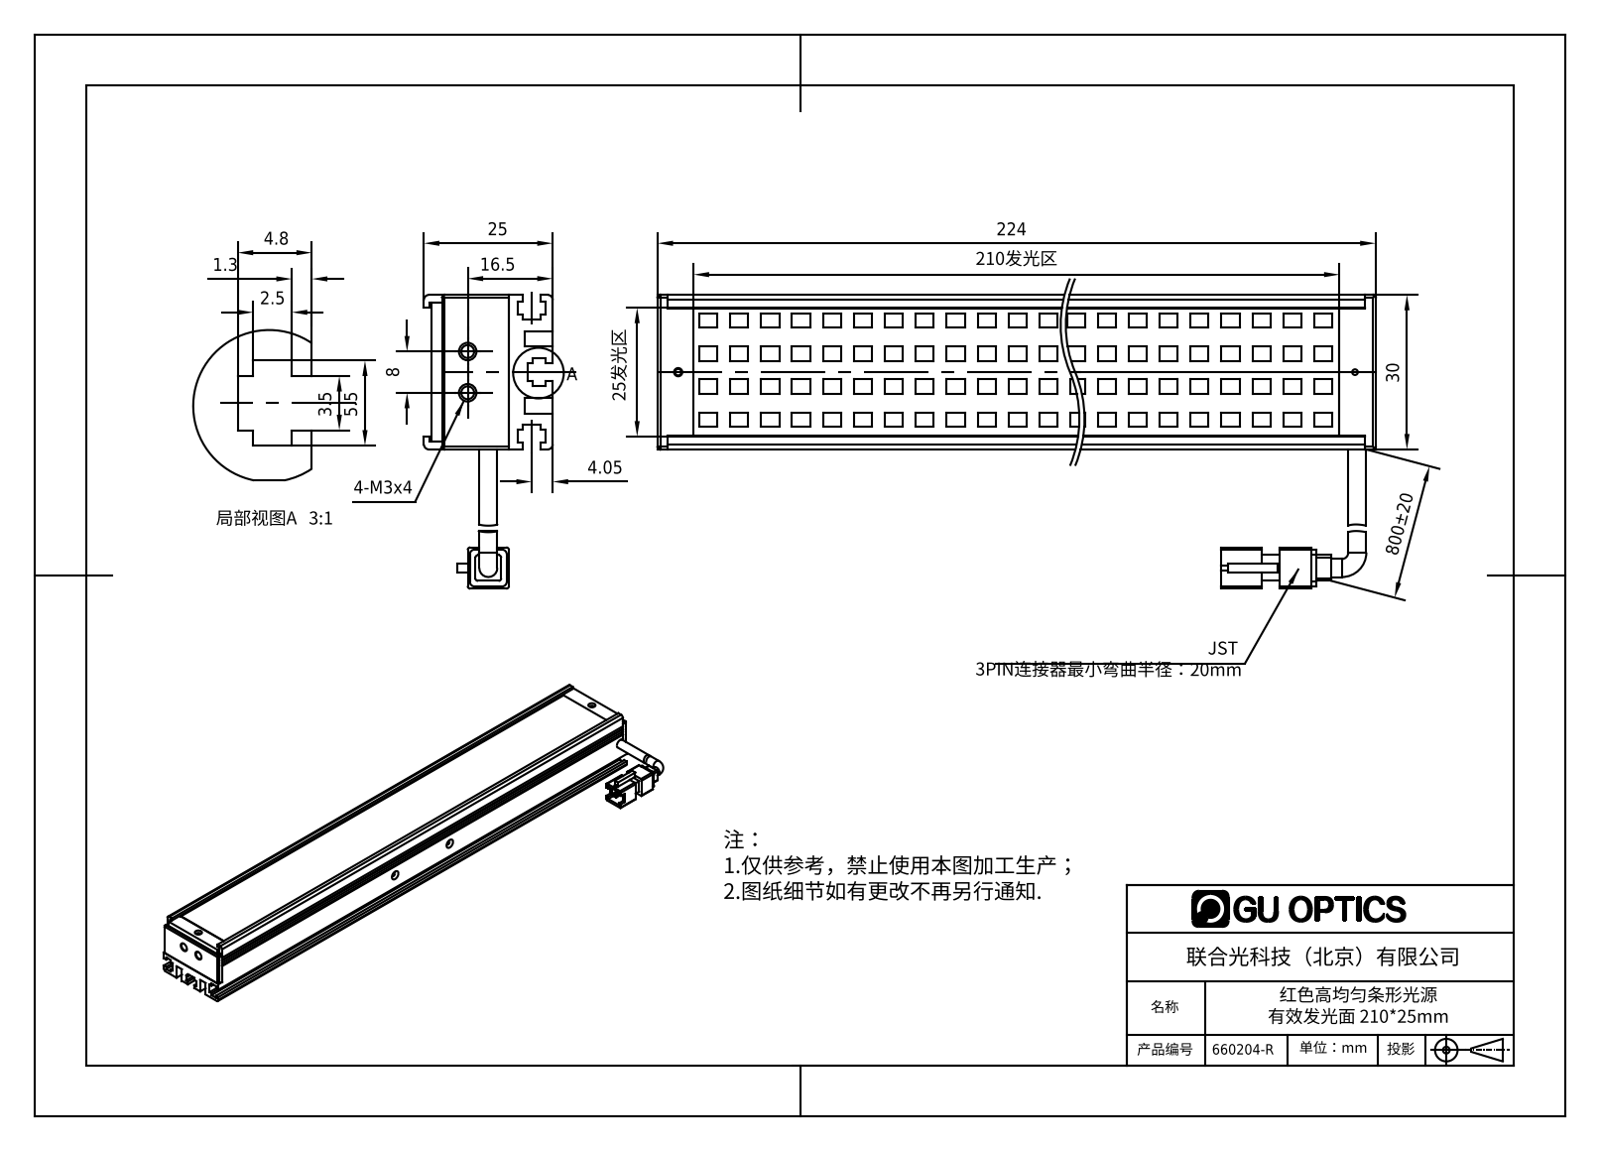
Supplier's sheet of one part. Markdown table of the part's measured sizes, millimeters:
| quantity | value |
| --- | --- |
| part name | 660204-R |
| STEP written by | SolidWorks 2016 (AUTOMOTIVE_DESIGN) |
| units | millimeters |
| bodies | 6 solids, 1144 faces (958 planar, 83 cylindrical, 103 other) |
| overall size | 224 × 57 × 25 |
| volume | 77 133 mm³ |
| surface area | 78 469 mm² |
| round holes (diameter × count) | 1.6 × 5, 1.5 × 2, 1.7 × 2, 2.5 × 2, 2.8 × 2, 3 × 2, 1.1 × 1, 1.25 × 1, 2 × 1 |
| round bosses / shafts (diameter × count) | 3.5 × 2 |
| partial cylindrical surfaces (radius × count) | 1 × 12, 0.5 × 8, 1.65 × 1 |
| main face-to-face distances | 1, 13, 2, 2.5, 3, 27.5, 9.5, 4.5, 12, 8.5 |
| hole center spacings | 216, 7, 93, 93.23, 123, 123.18, 216.11, 8 |
